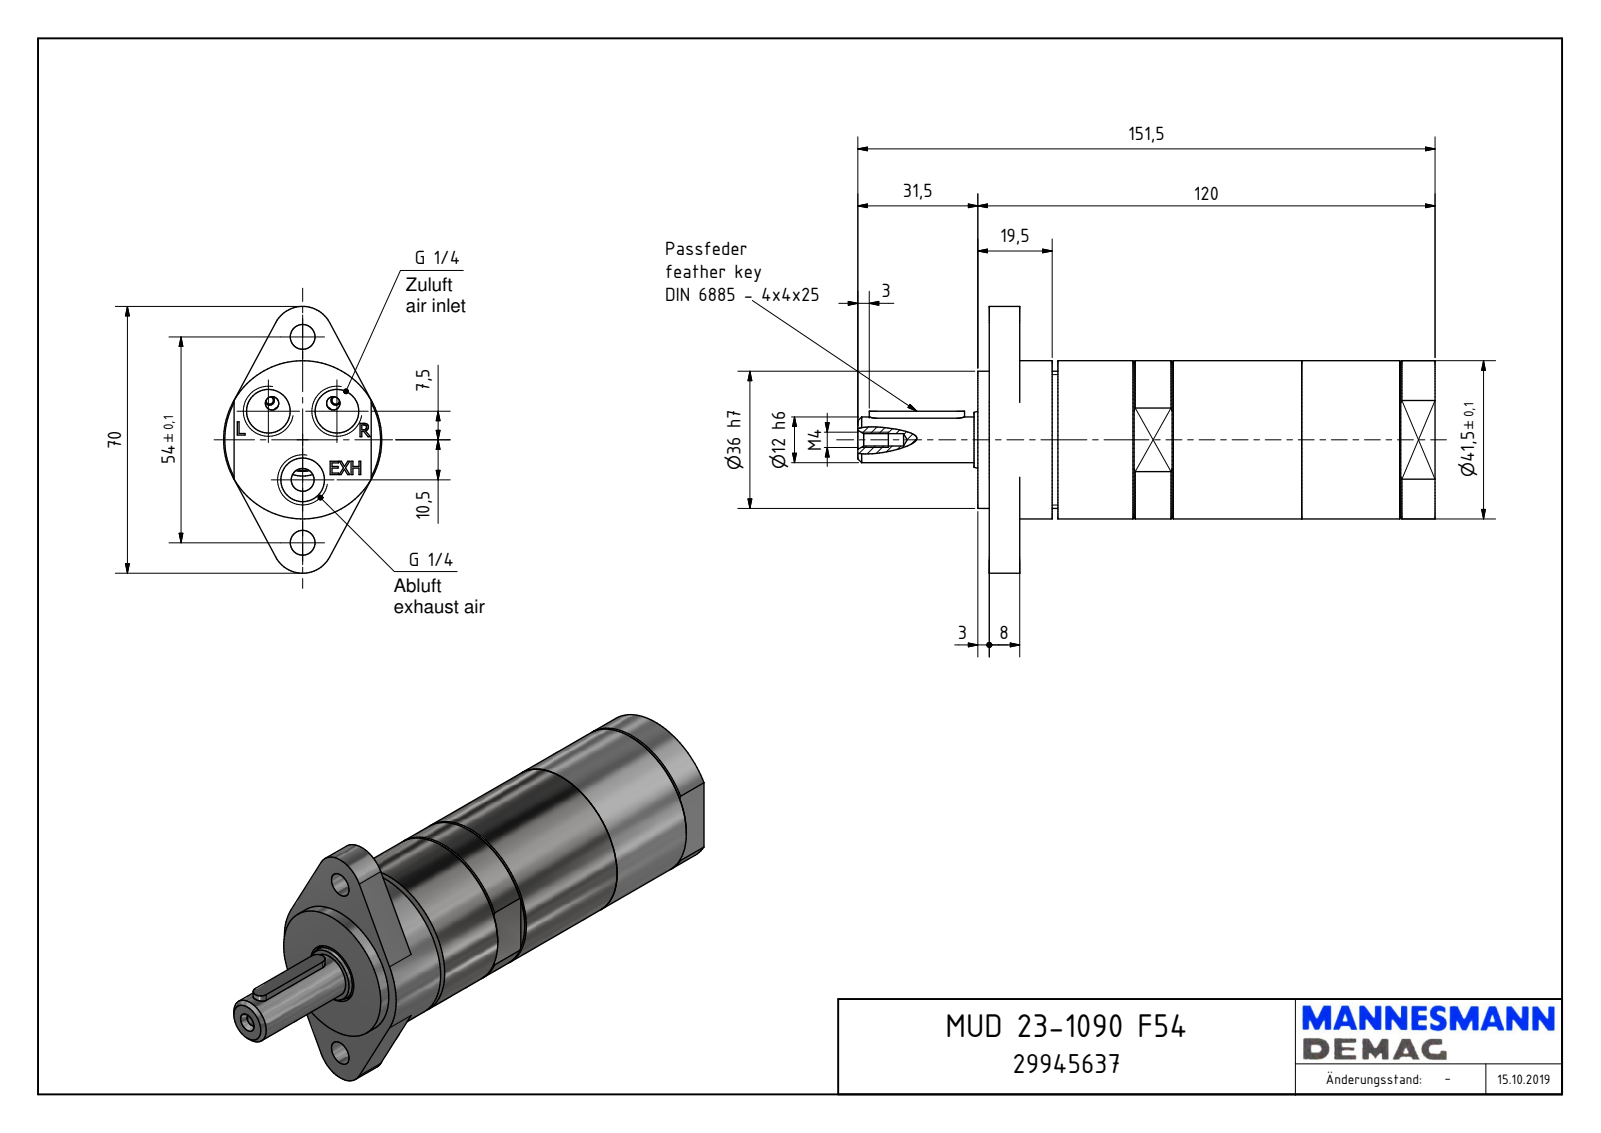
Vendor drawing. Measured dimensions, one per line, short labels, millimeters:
name: MUD 23-1090_29945637
written by: Autodesk Inventor 2018 (AUTOMOTIVE_DESIGN)
unit: mm
bodies: 1 solid, 135 faces (89 planar, 23 cylindrical, 23 other)
size: 151.5 × 70 × 41.5
volume: 164 092 mm³; area: 23 255 mm²
holes: 3× ⌀11.45, 2× ⌀6.5, 1× ⌀3.24, 1× ⌀16
bosses: 1× ⌀41.5, 1× ⌀36, 1× ⌀14.95, 1× ⌀12
rounds: 2× R2, 2× R8
face distances: 117, 3, 120, 11, 8, 109, 21, 1, 41.48, 10
hole spacings: 11.72, 20.12, 21.48, 27, 35.65, 10.5, 16.5, 18
